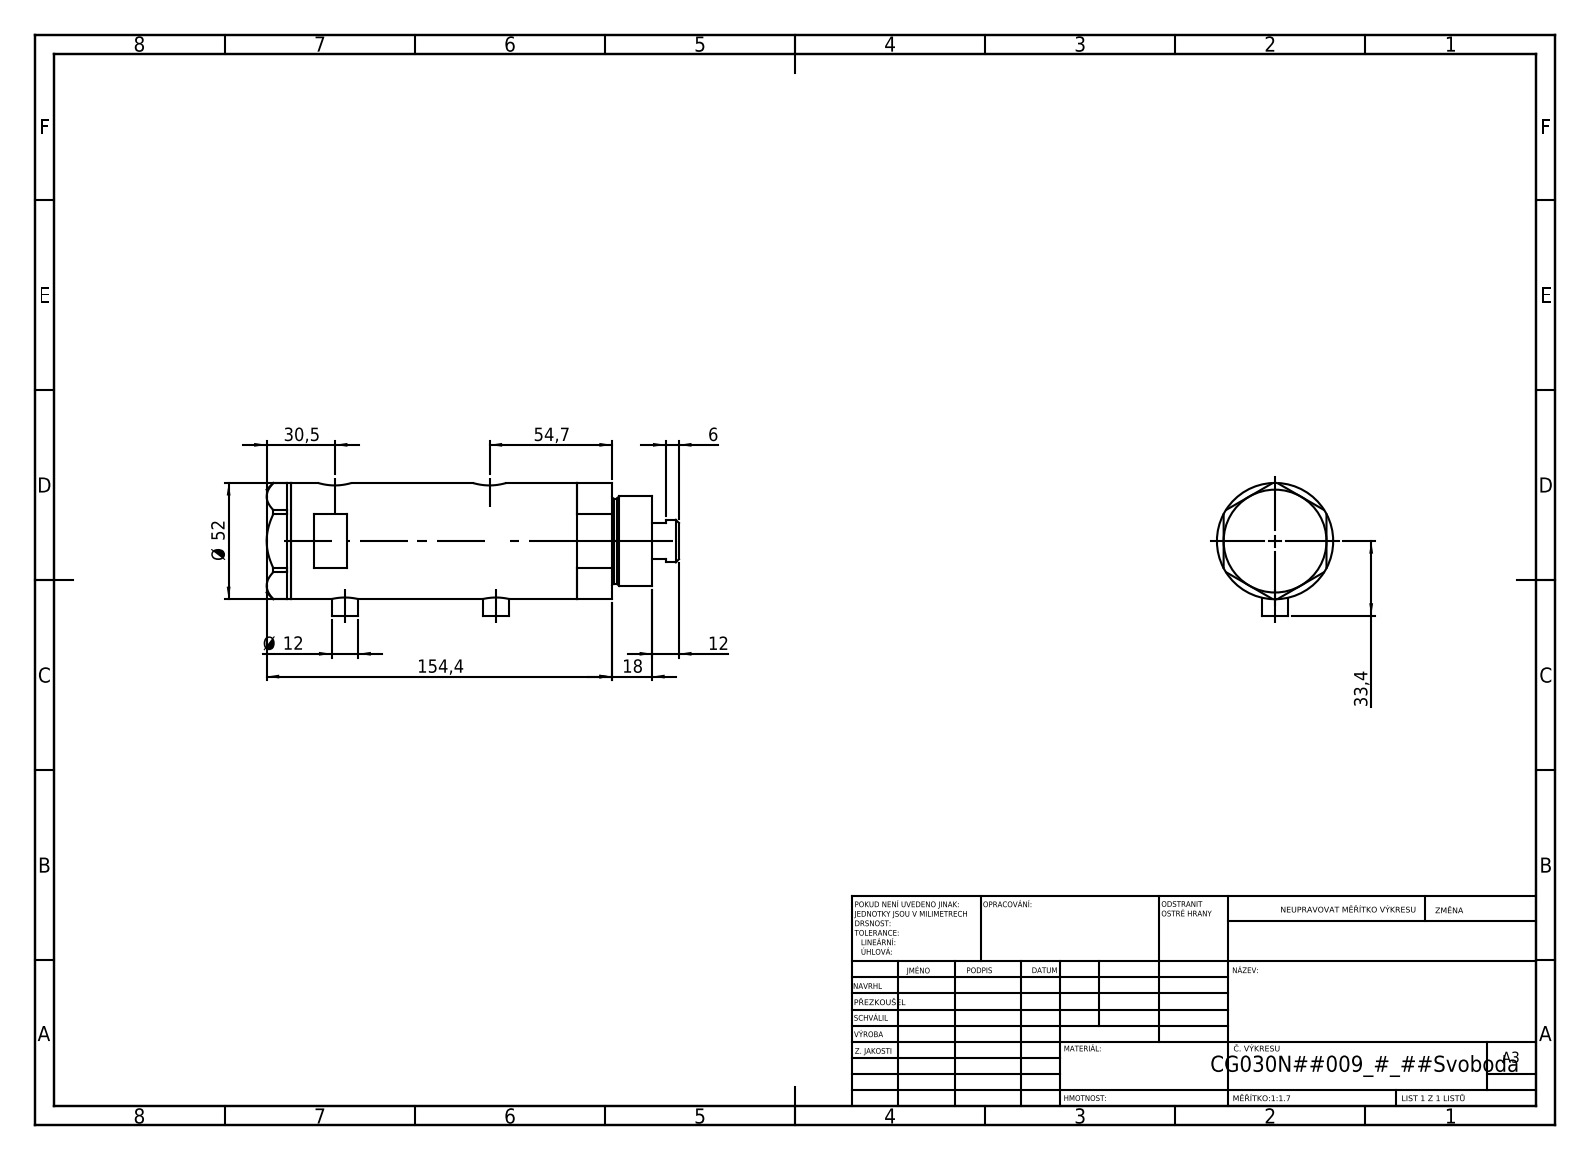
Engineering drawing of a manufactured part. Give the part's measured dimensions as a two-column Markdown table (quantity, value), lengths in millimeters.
| quantity | value |
| --- | --- |
| part name | V270CG_VC; V270CG_FRONT; V270CG_BACK; V270CG_MIDDLE |
| STEP written by | SolidWorks 2019 (CONFIG_CONTROL_DESIGN) |
| units | millimeters |
| bodies | 4 solids, 140 faces (67 planar, 53 cylindrical, 20 other) |
| overall size | 184.4 × 59.4 × 52 |
| volume | 342 528 mm³ |
| surface area | 78 187 mm² |
| round holes (diameter × count) | 5 × 2, 9.73 × 2, 12.5 × 2, 15 × 2, 6.5 × 1, 20 × 1, 21.5 × 1, 30 × 1, 33 × 1, 44 × 1 |
| round bosses / shafts (diameter × count) | 12 × 2, 52 × 1, 40 × 1, 38 × 1, 19 × 1 |
| main face-to-face distances | 91.5, 23.8, 67.7, 11, 34.8, 102.5, 46, 138.9, 127.9, 104.1 |
| hole center spacings | 2.9, 4.5, 64.7, 67.6, 69.2, 72.1 |
